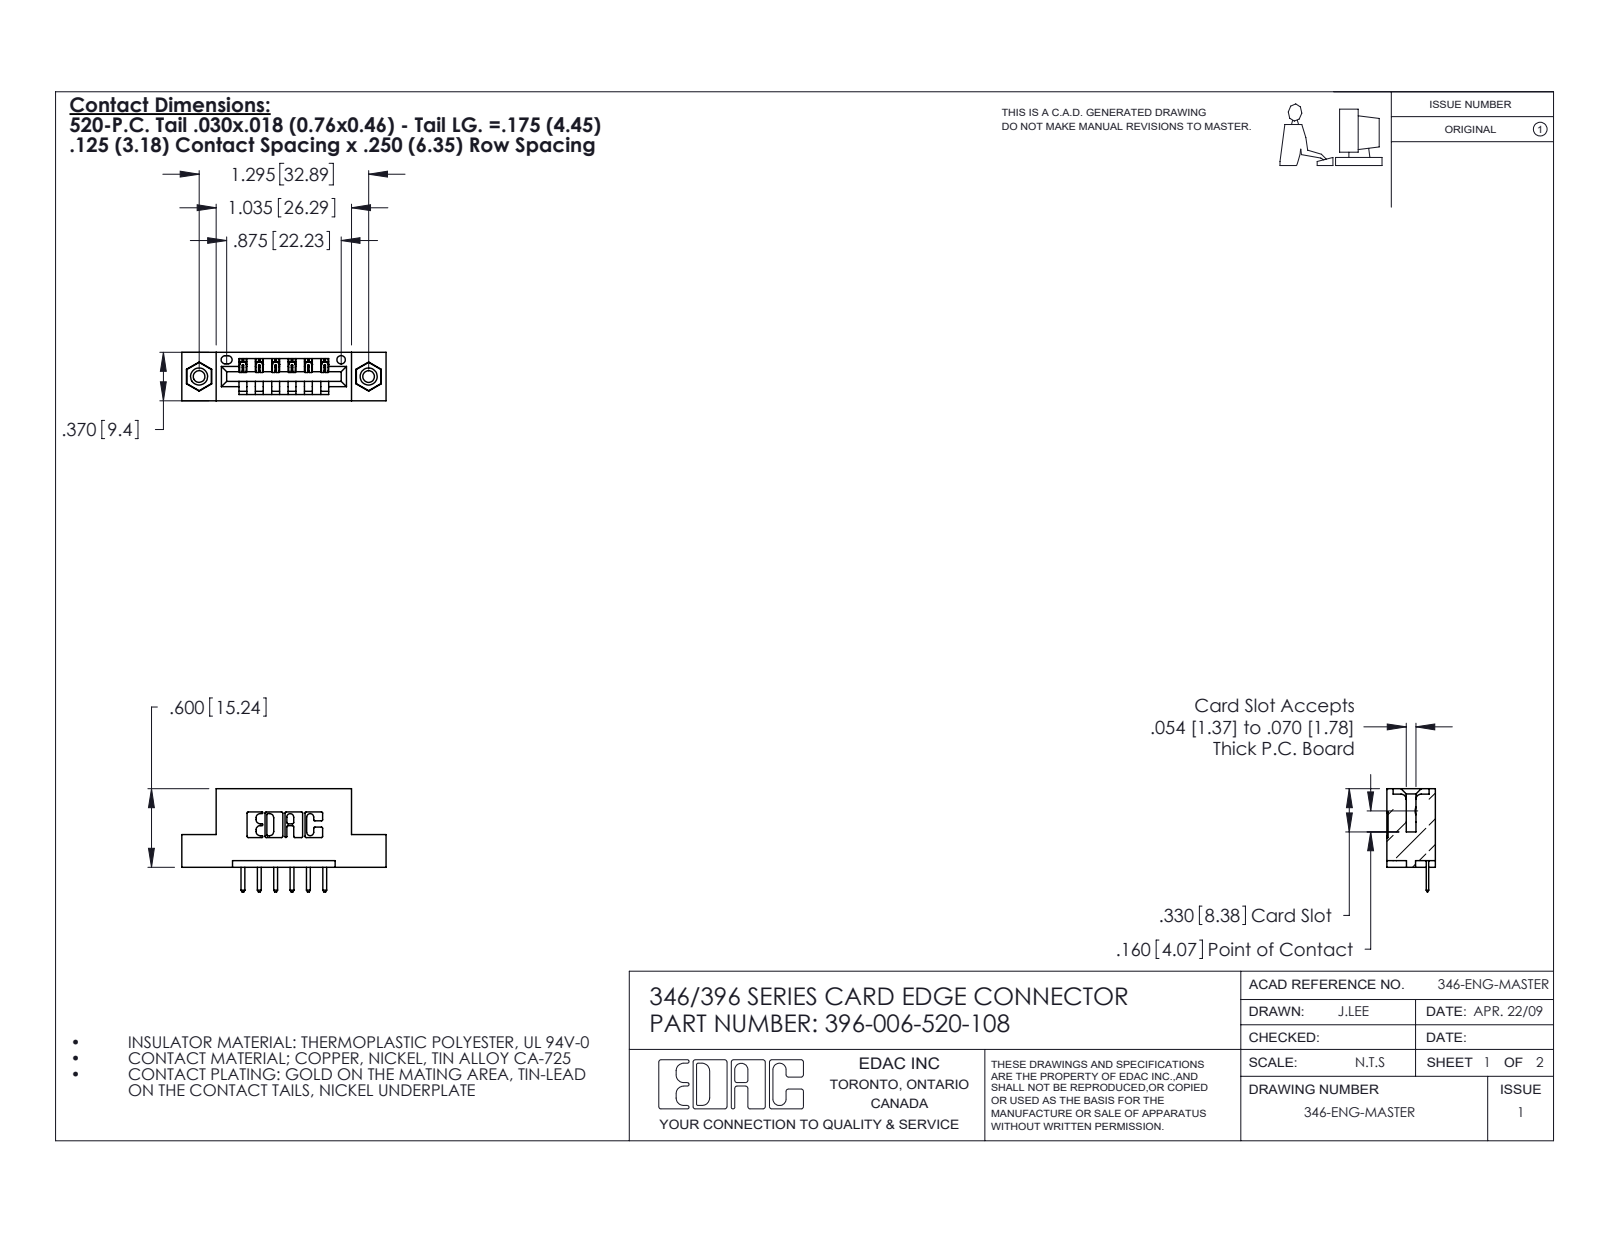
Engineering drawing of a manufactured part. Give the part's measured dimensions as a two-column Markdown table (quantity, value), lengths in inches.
| quantity | value |
| --- | --- |
| part name | 345-292-001_345-293-120; 346 Part_Flush Mounting Lugs - 0.156 Dia-TI; 345-250-001_345-250-003-102; 396-006-520-108 |
| STEP written by | SolidWorks 2020 (CONFIG_CONTROL_DESIGN) |
| units | inches |
| bodies | 9 solids, 554 faces (360 planar, 178 cylindrical, 16 other) |
| overall size | 1.56 × 0.788 × 0.37 |
| volume | 0.215 in³ |
| surface area | 6.164 in² |
| round holes (diameter × count) | 0.089 × 2, 0.125 × 2, 0.156 × 2, 0.064 × 1 |
| round bosses / shafts (diameter × count) | 0.155 × 2 |
| partial cylindrical surfaces (radius × count) | 0.01 × 22, 0.01 × 14, 0.006 × 12, 0.007 × 6, 0.031 × 6, 0.026 × 3, 0.031 × 2, 0.04 × 2 |
| main face-to-face distances | 0.25, 0.37, 0.048, 0.322, 0.148, 0.222, 0.1, 0.174, 0.125, 0.125 |
| hole center spacings | 0.246, 1.092, 1.295 |
